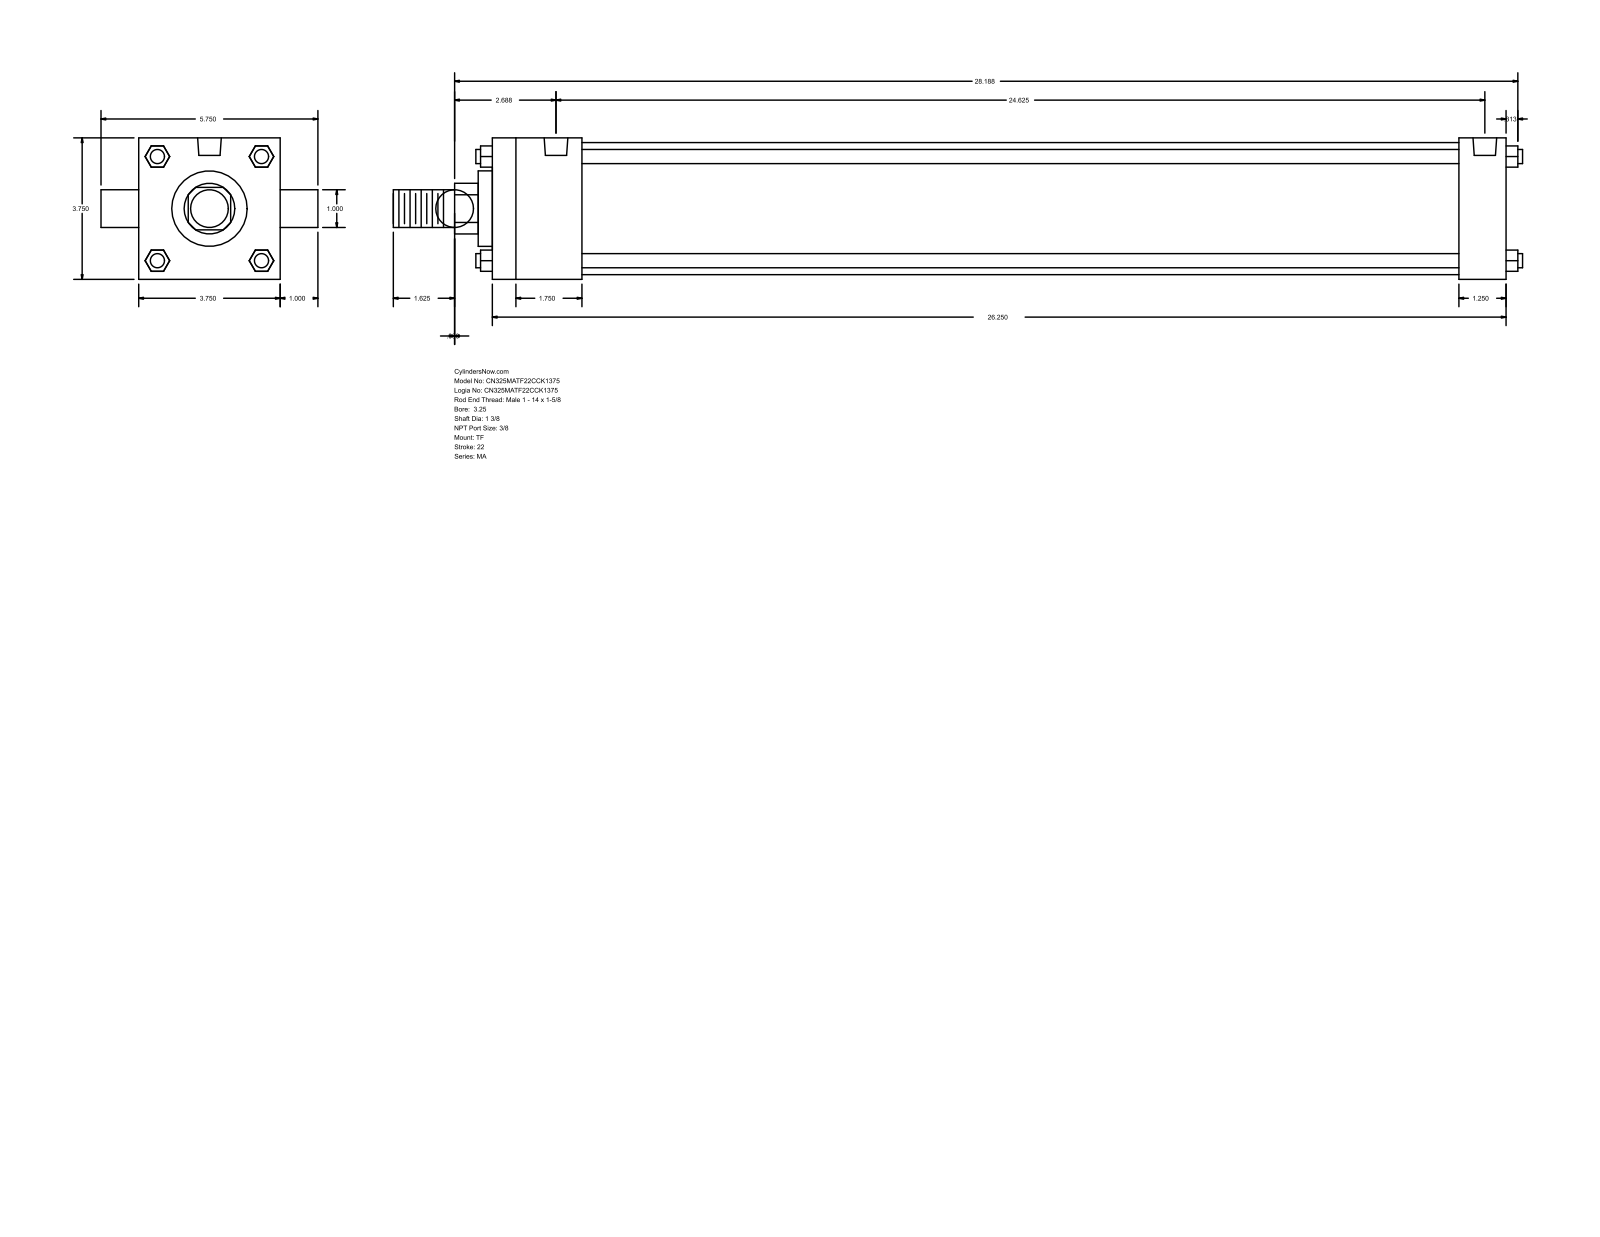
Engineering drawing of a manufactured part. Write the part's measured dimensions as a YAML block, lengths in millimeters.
part_name: "MA_TF__0325_1.375"
step_written_by: "GSSL Pune (CONFIG_CONTROL_DESIGN)"
units: millimeters
bodies: {solids: 0, faces: 120, planar: 92, cylindrical: 28, other: 0}
overall_size: [760.41, 146.05, 95.25]
round_holes:
  - {diameter: 11.11, count: 3}
  - {diameter: 15.93, count: 2}
round_bosses_or_shafts:
  - {diameter: 9.53, count: 4}
  - {diameter: 25.4, count: 2}
  - {diameter: 88.9, count: 1}
  - {diameter: 50.8, count: 1}
  - {diameter: 34.92, count: 1}
partial_cylinders:
  - {radius: 17.06, count: 1}
face_to_face_distances: [95.24, 682.62, 60.32, 650.87, 590.55, 622.3, 31.75, 9.52, 69.84, 660.39]
hole_center_spacings: [4.76, 4.77, 615.95, 620.71, 620.72, 625.48]
